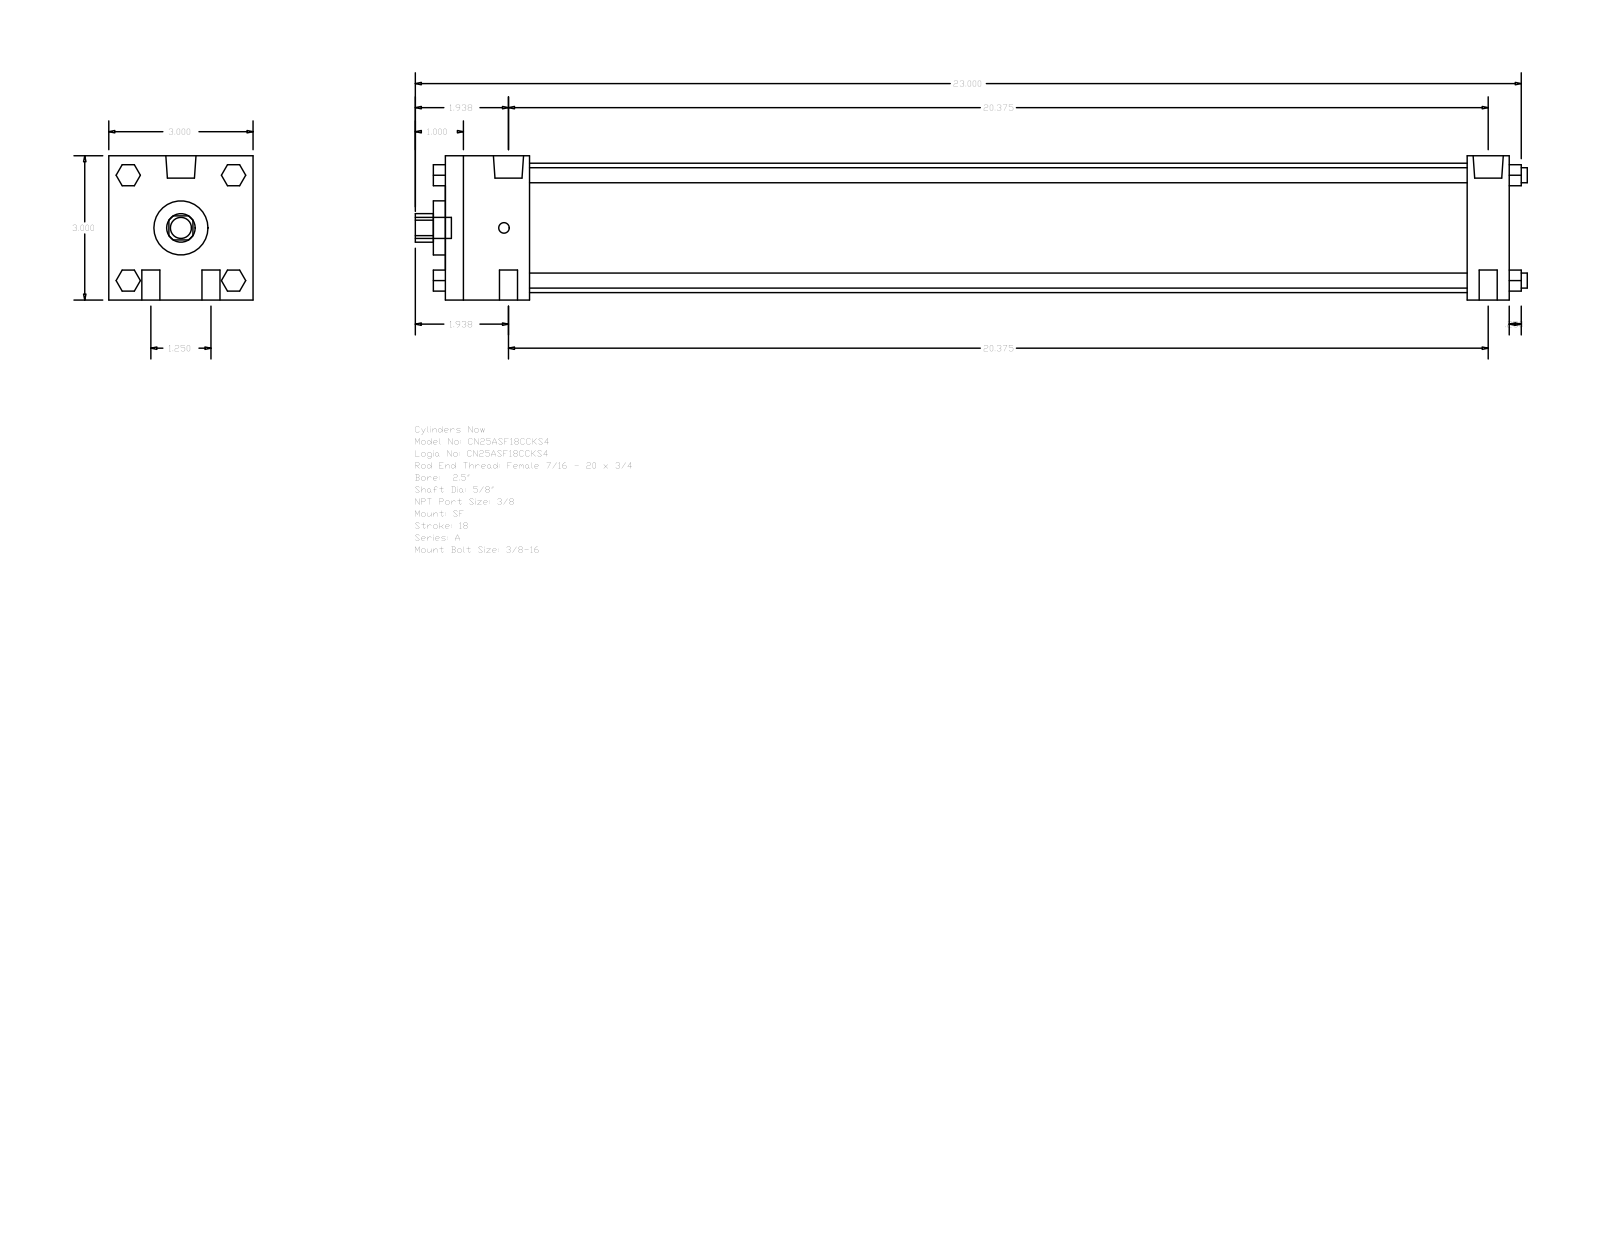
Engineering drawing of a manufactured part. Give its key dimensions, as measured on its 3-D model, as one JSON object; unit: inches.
{"part_name": "A_SF__0250_0.625", "step_written_by": "GSSL Pune (CONFIG_CONTROL_DESIGN)", "units": "inches", "bodies": {"solids": 0, "faces": 124, "planar": 94, "cylindrical": 30, "other": 0}, "overall_size": [23.125, 3, 3], "round_holes": [[0.625, 1], [1.125, 1], [2.69, 1]], "round_bosses_or_shafts": [[0.375, 4], [0.313, 4], [0.627, 2], [0.219, 2], [0.437, 1]], "partial_cylinders_radius": [[0.297, 1]], "face_to_face_distances": [3, 22.125, 1.75, 21.25, 0.875, 19.5, 20.375, 0.25, 22.375, 2]}
